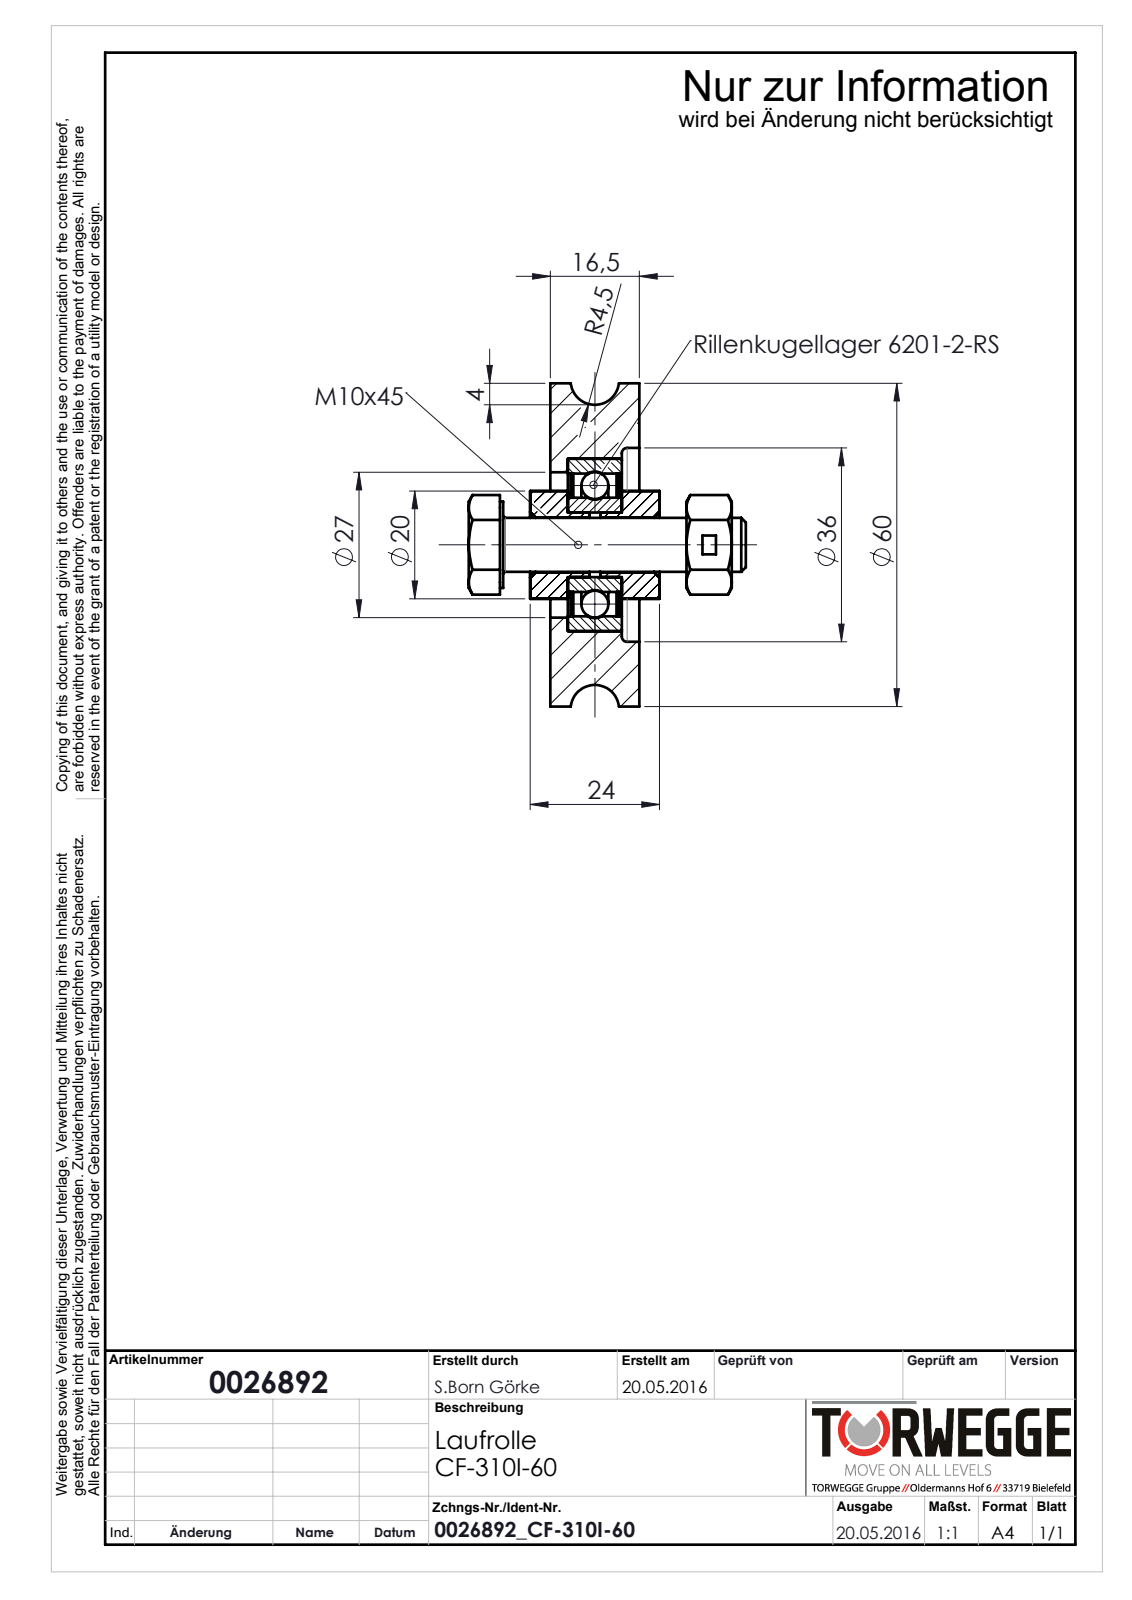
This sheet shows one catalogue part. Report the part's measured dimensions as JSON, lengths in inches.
{"part_name": "0026892_Laufrolle; 0026892_CF-310I-60; hex nut style 1 gradeab_din_Hexagon Nut ISO 4032 - M10 - D - N; hex bolt gradeab_din_ISO 4014 - M10 x 60 x 26-N (+1 more)", "step_written_by": "SolidWorks 2018 (AUTOMOTIVE_DESIGN)", "units": "inches", "bodies": {"solids": 8, "faces": 123, "planar": 35, "cylindrical": 38, "other": 50}, "overall_size": [2.614, 2.362, 2.362], "volume_in3": 2.531, "surface_area_in2": 30.07, "round_holes": [[0.335, 1], [0.394, 1], [0.472, 1], [0.689, 1], [1.043, 1], [1.063, 1], [1.26, 1], [1.417, 1]], "round_bosses_or_shafts": [[2.362, 1], [0.63, 1]], "face_to_face_distances": [0.65, 0.02, 0.128, 0.522, 0.354, 0.148, 0.167, 0.482, 0.502, 0.039]}
